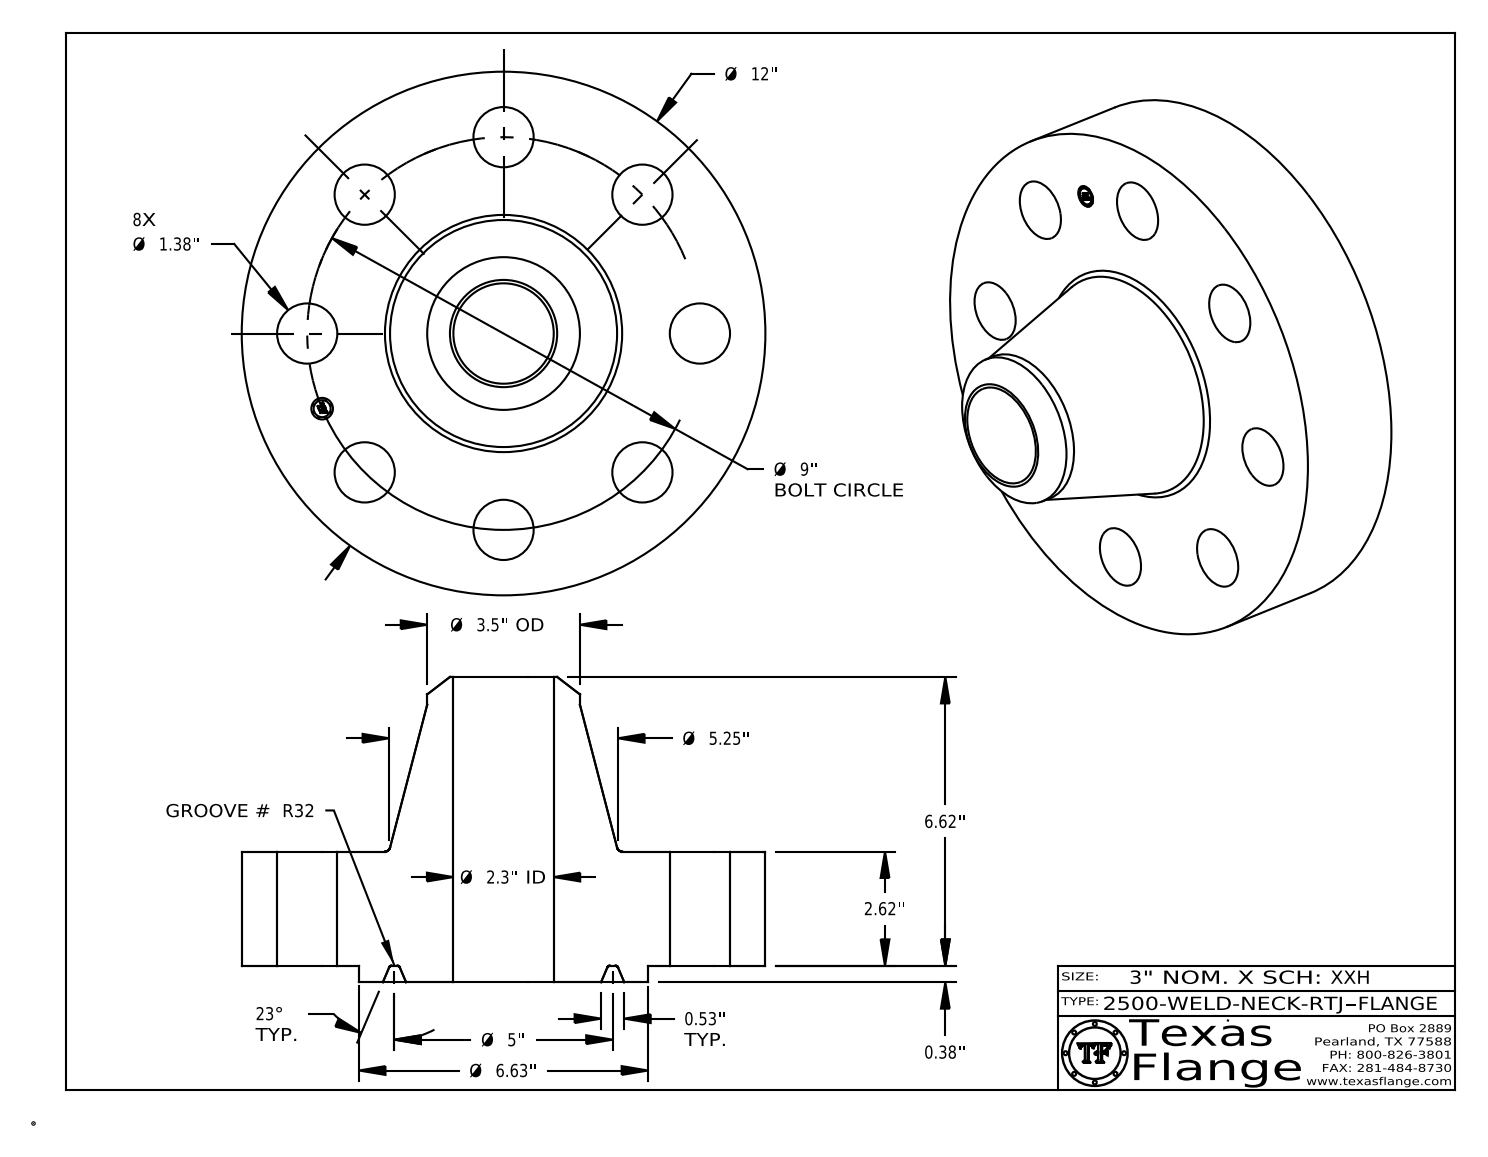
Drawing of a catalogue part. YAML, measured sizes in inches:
part_name: "2500-WELD-NECK-RTJ"
step_written_by: "CATIA V5 STEP AP214 (AUTOMOTIVE_DESIGN)"
units: inches
bodies: {solids: 1, faces: 429, planar: 371, cylindrical: 44, other: 14}
overall_size: [12, 12, 6.995]
volume: 303
surface_area: 488.7
round_holes:
  - {diameter: 1.38, count: 8}
  - {diameter: 0.495, count: 1}
  - {diameter: 2.3, count: 1}
round_bosses_or_shafts:
  - {diameter: 0.03, count: 8}
  - {diameter: 12, count: 1}
  - {diameter: 6.625, count: 1}
  - {diameter: 3.5, count: 1}
  - {diameter: 0.39, count: 1}
face_to_face_distances: [2.62, 0.375, 2.995, 6.995, 6.62, 4, 2.98, 2.605, 0.015, 4.015]
hole_center_spacings: [4.5, 3.444, 6.364, 8.315, 1.756, 5, 7.483, 9]
